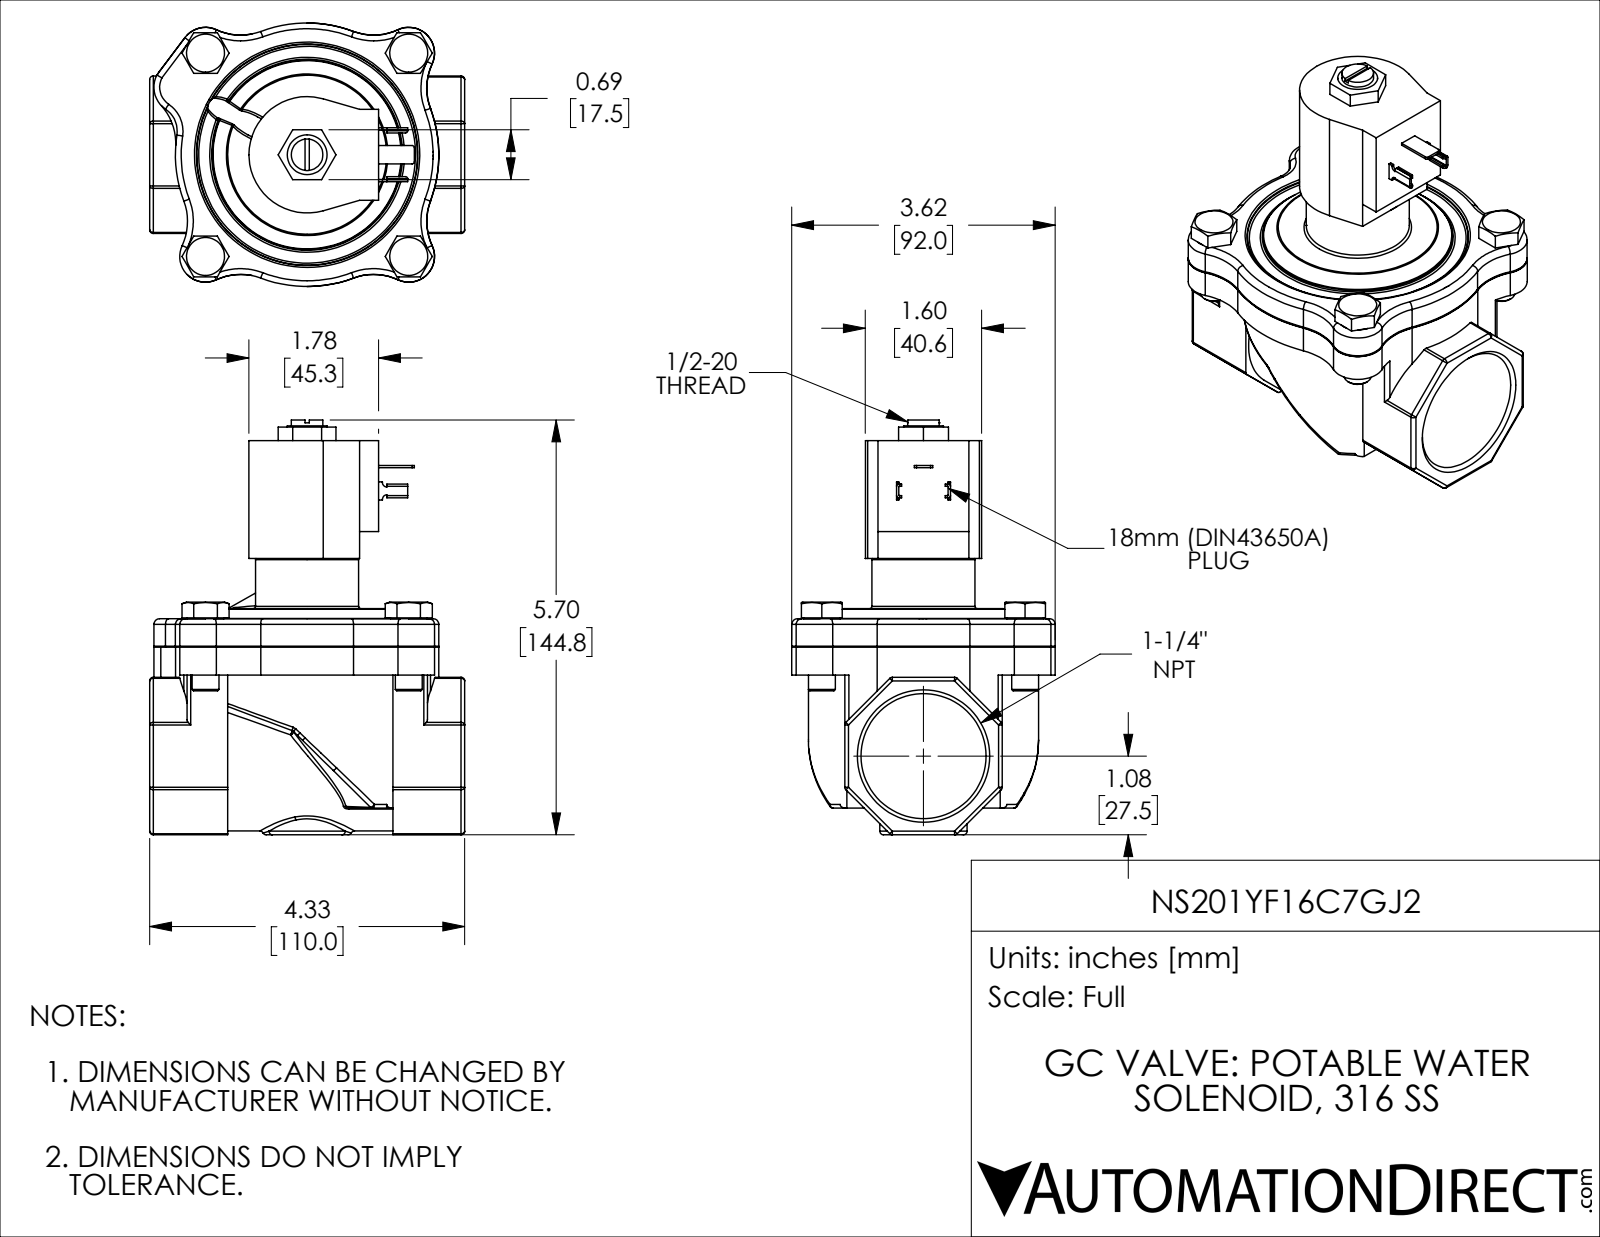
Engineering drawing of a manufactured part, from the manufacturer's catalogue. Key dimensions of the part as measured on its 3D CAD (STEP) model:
Part name (STEP PRODUCT): NS201YF16C7GJ2
STEP written by: SolidWorks 2018 (AUTOMOTIVE_DESIGN)
Units: inches
Bodies: 12 solids, 524 faces (166 planar, 159 cylindrical, 199 other)
Overall size (bounding box): 5.701 × 4.33 × 3.622
Volume: 27.06 in³ · Surface area: 137.5 in²
Round holes (diameter × count): ⌀0.375 ×4, ⌀0.433 ×4, ⌀0.125 ×1, ⌀0.488 ×1, ⌀0.846 ×1, ⌀0.949 ×1, ⌀1.718 ×1
Round bosses / shafts (diameter × count): ⌀0.504 ×4, ⌀0.37 ×4, ⌀1.417 ×1, ⌀0.547 ×1, ⌀0.434 ×1
Partial cylindrical surfaces — rounded edges, fillets, slot ends (radius × count): R0.05 ×30, R0.787 ×15, R0.03 ×8, R0.354 ×8, R0.362 ×2, R1.811 ×2, R0.031 ×1, R0.079 ×1
Main face-to-face distances: 0.393, 2.84, 2.447, 1.22, 0.827, 1.62, 2.578, 2.97, 3.798, 5.418
Hole centre spacings: 2.795, 1.976, 1.977, 2.794, 2.795, 3.952, 3.953
